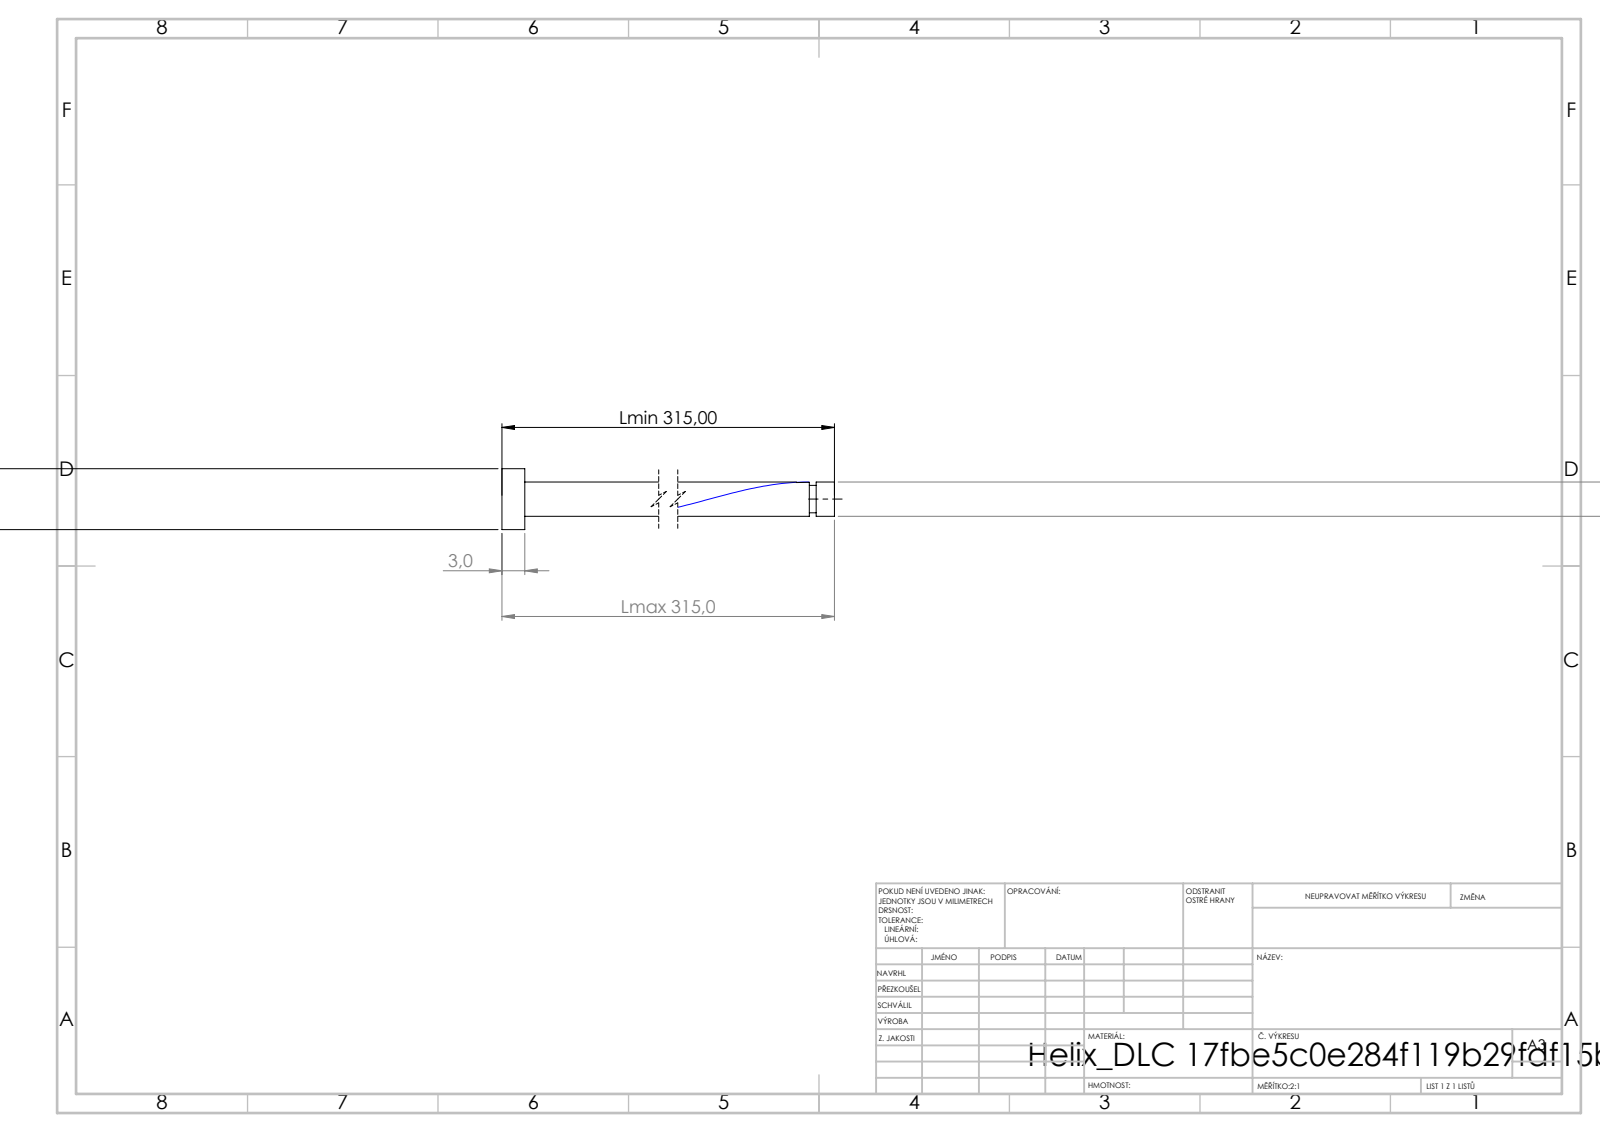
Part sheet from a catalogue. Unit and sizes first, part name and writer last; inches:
Units: inches
Overall size (bounding box): 12.402 × 0.315 × 0.315
Round bosses / shafts (diameter × count): ⌀0.315 ×1, ⌀0.177 ×1, ⌀0.142 ×1
Main face-to-face distances: 0.118, 12.402, 12.283, 12.307, 12.189, 0.095, 12.271, 12.153, 0.035, 0.13
Volume: 0.377 in³ · Surface area: 9.533 in²
Bodies: 1 solid, 16 faces (6 planar, 9 cylindrical, 1 other)
STEP written by: SolidWorks 2019 (CONFIG_CONTROL_DESIGN)
